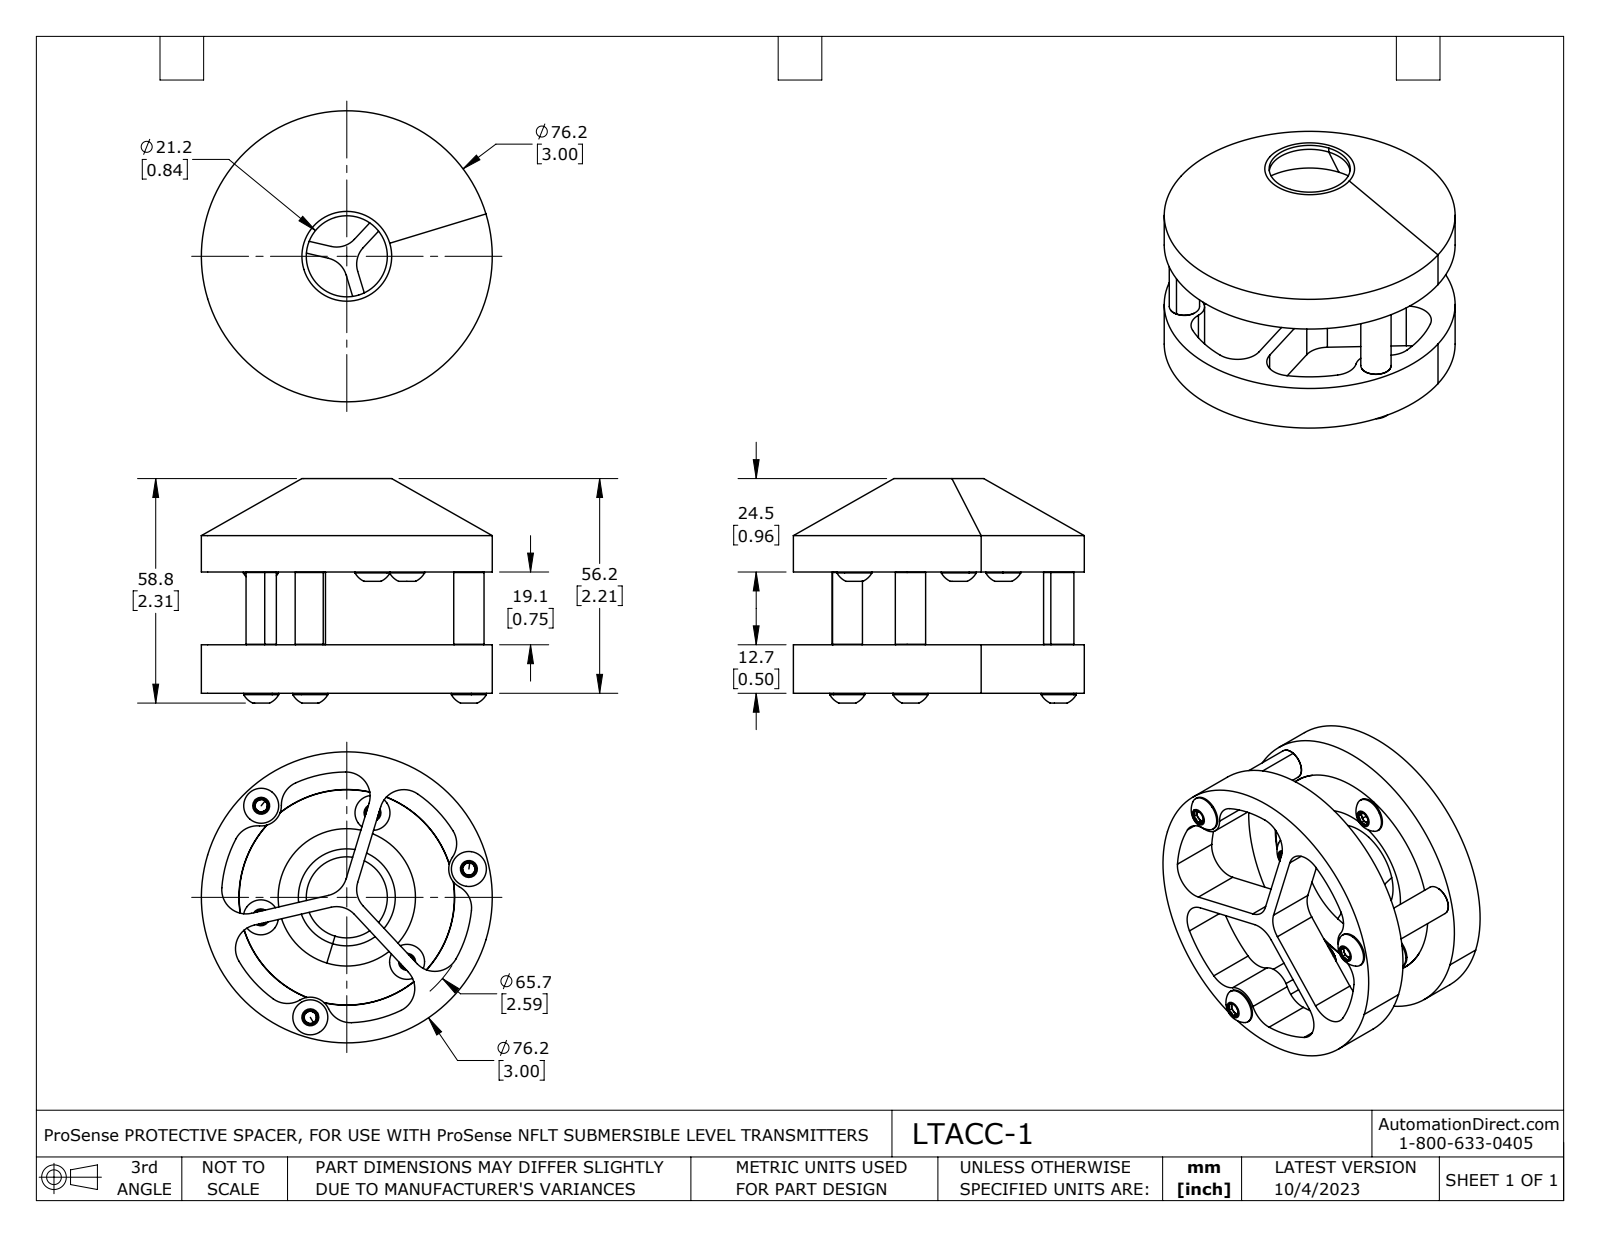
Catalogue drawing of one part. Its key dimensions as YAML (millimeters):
part_name: "LTACC-1"
step_written_by: "SolidWorks 2021 (AUTOMOTIVE_DESIGN)"
units: millimeters
bodies: {solids: 1, faces: 233, planar: 91, cylindrical: 61, other: 81}
overall_size: [76.2, 76.2, 58.8]
volume: 83670
surface_area: 27410
round_holes:
  - {diameter: 21.2, count: 1}
  - {diameter: 25.4, count: 1}
  - {diameter: 32.5, count: 1}
  - {diameter: 56.5, count: 1}
round_bosses_or_shafts:
  - {diameter: 9.2, count: 6}
  - {diameter: 8, count: 3}
  - {diameter: 76.2, count: 1}
  - {diameter: 56.4, count: 1}
partial_cylinders:
  - {radius: 6.4, count: 15}
  - {radius: 5.3, count: 3}
  - {radius: 32.8, count: 1}
face_to_face_distances: [19.1, 12.7, 31.8, 31.9, 19.2, 3.2, 3.2, 34.9, 22.2, 3]
